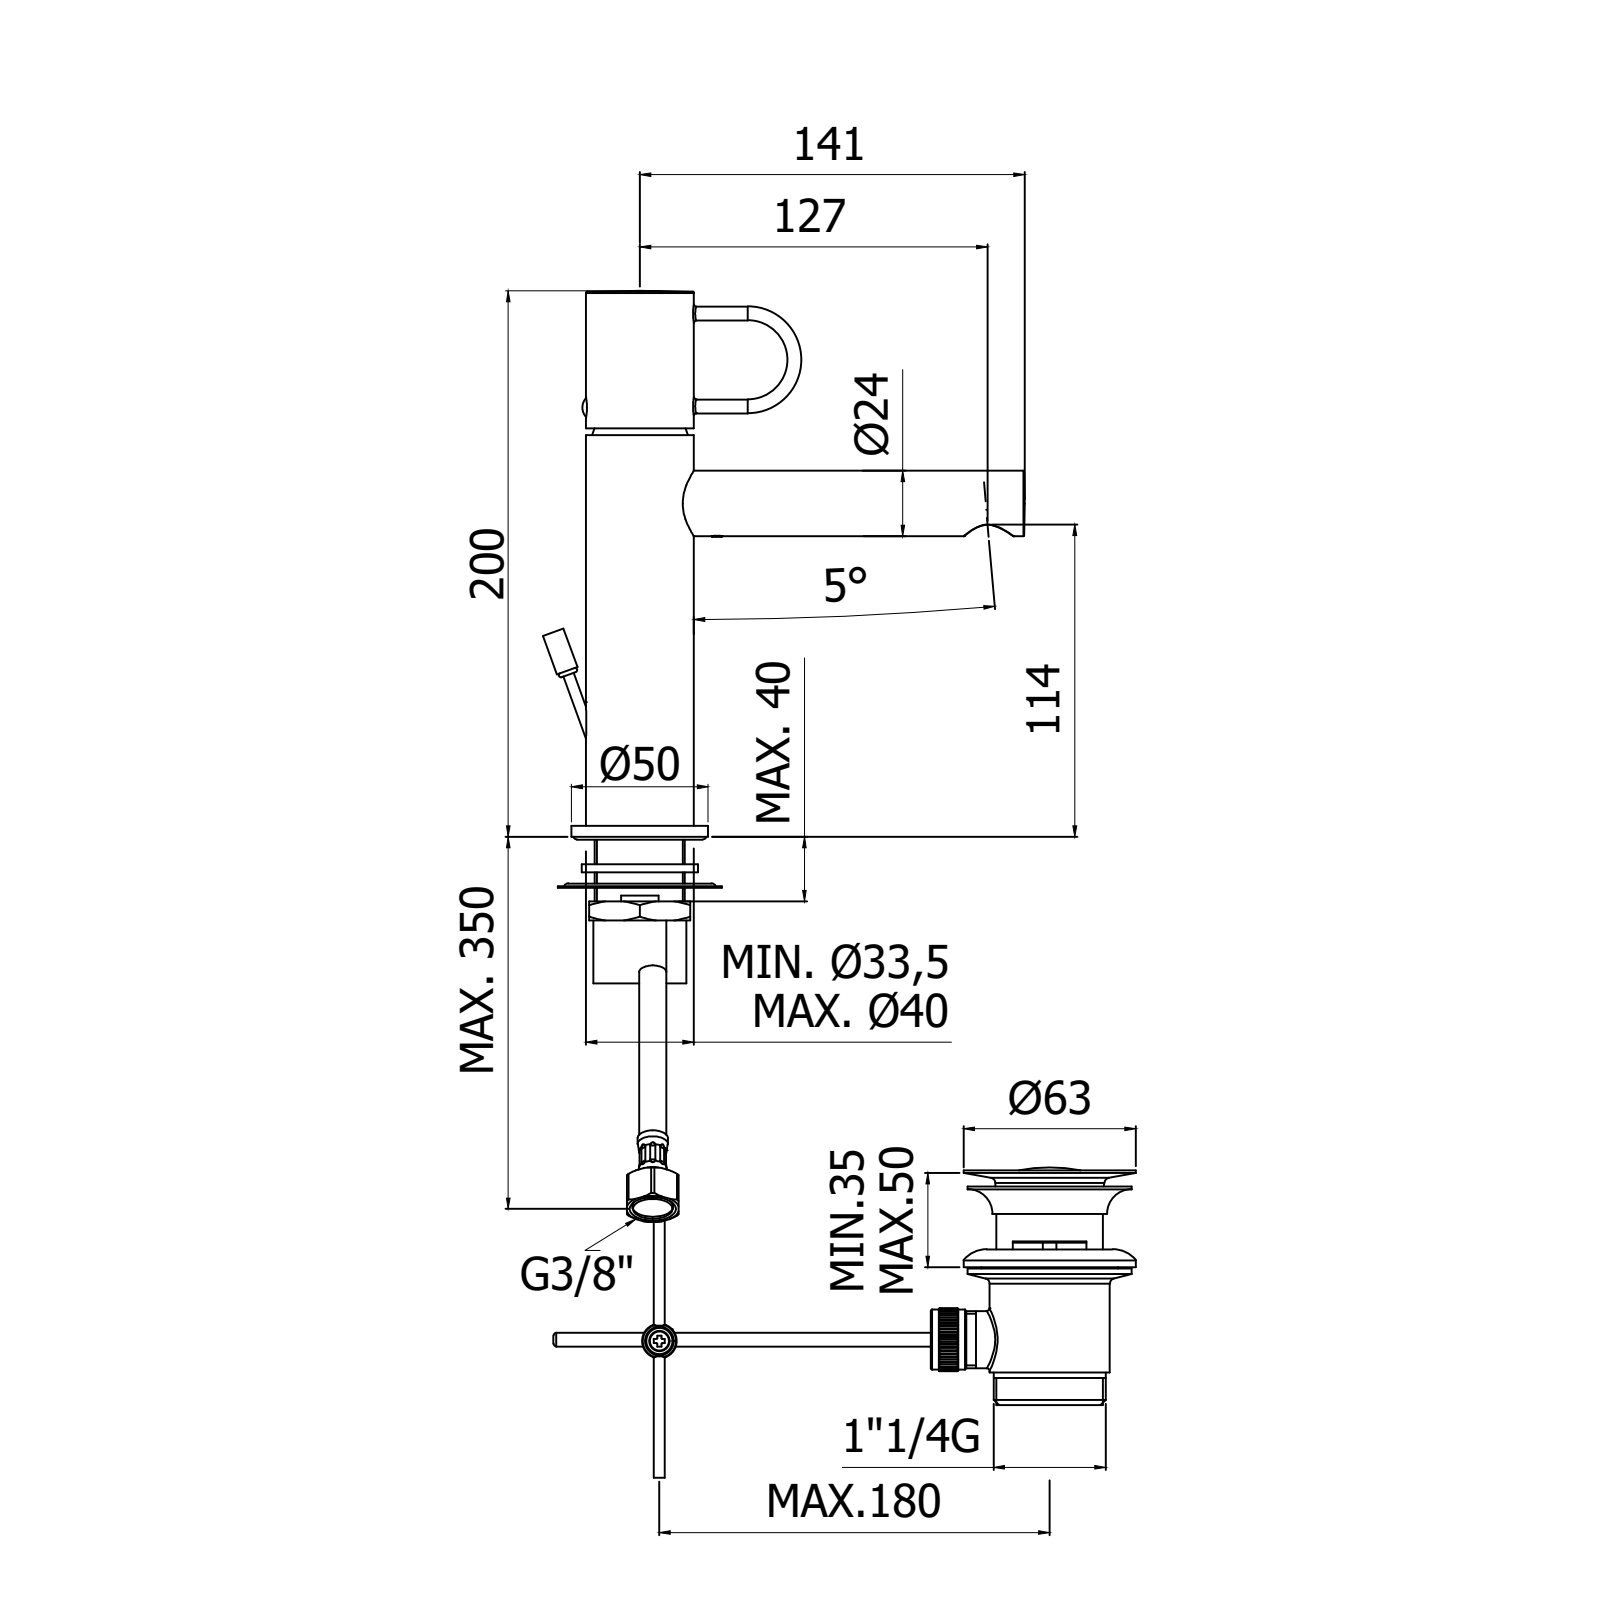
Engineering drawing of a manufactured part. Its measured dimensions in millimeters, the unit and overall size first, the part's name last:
Units: millimetres
Overall size (bounding box): 199.84 × 176.38 × 50
Round holes (diameter × count): ⌀5 ×3, ⌀7 ×3, ⌀3.2 ×2, ⌀6.5 ×2, ⌀9.4 ×2, ⌀11 ×2, ⌀3 ×1, ⌀4.2 ×1, ⌀5.5 ×1, ⌀8 ×1, ⌀12.15 ×1, ⌀12.45 ×1
Round bosses / shafts (diameter × count): ⌀5 ×3, ⌀4 ×3, ⌀0.9 ×3, ⌀11 ×2, ⌀10 ×2, ⌀9 ×2, ⌀8 ×2, ⌀50 ×1
Partial cylindrical surfaces — rounded edges, fillets, slot ends (radius × count): R0.12 ×51, R3 ×28, R0.5 ×18, R0.2 ×8, R1 ×5, R0.6 ×4, R2 ×4, R3.5 ×3
Main face-to-face distances: 4, 2, 197.5, 193.5, 50.5, 6.5, 96.5, 92.5, 101, 14.8
Hole centre spacings: 1.5, 6.72, 7.85, 8.92, 8.94, 9.33, 11, 15.46
Volume: 152 304 mm³ · Surface area: 96 479 mm²
Bodies: 4 solids, 2934 faces (1941 planar, 625 cylindrical, 368 other)
Part name (STEP PRODUCT): JK075CR
STEP written by: CREO PARAMETRIC BY PTC INC, 2020044 (CONFIG_CONTROL_DESIGN)
